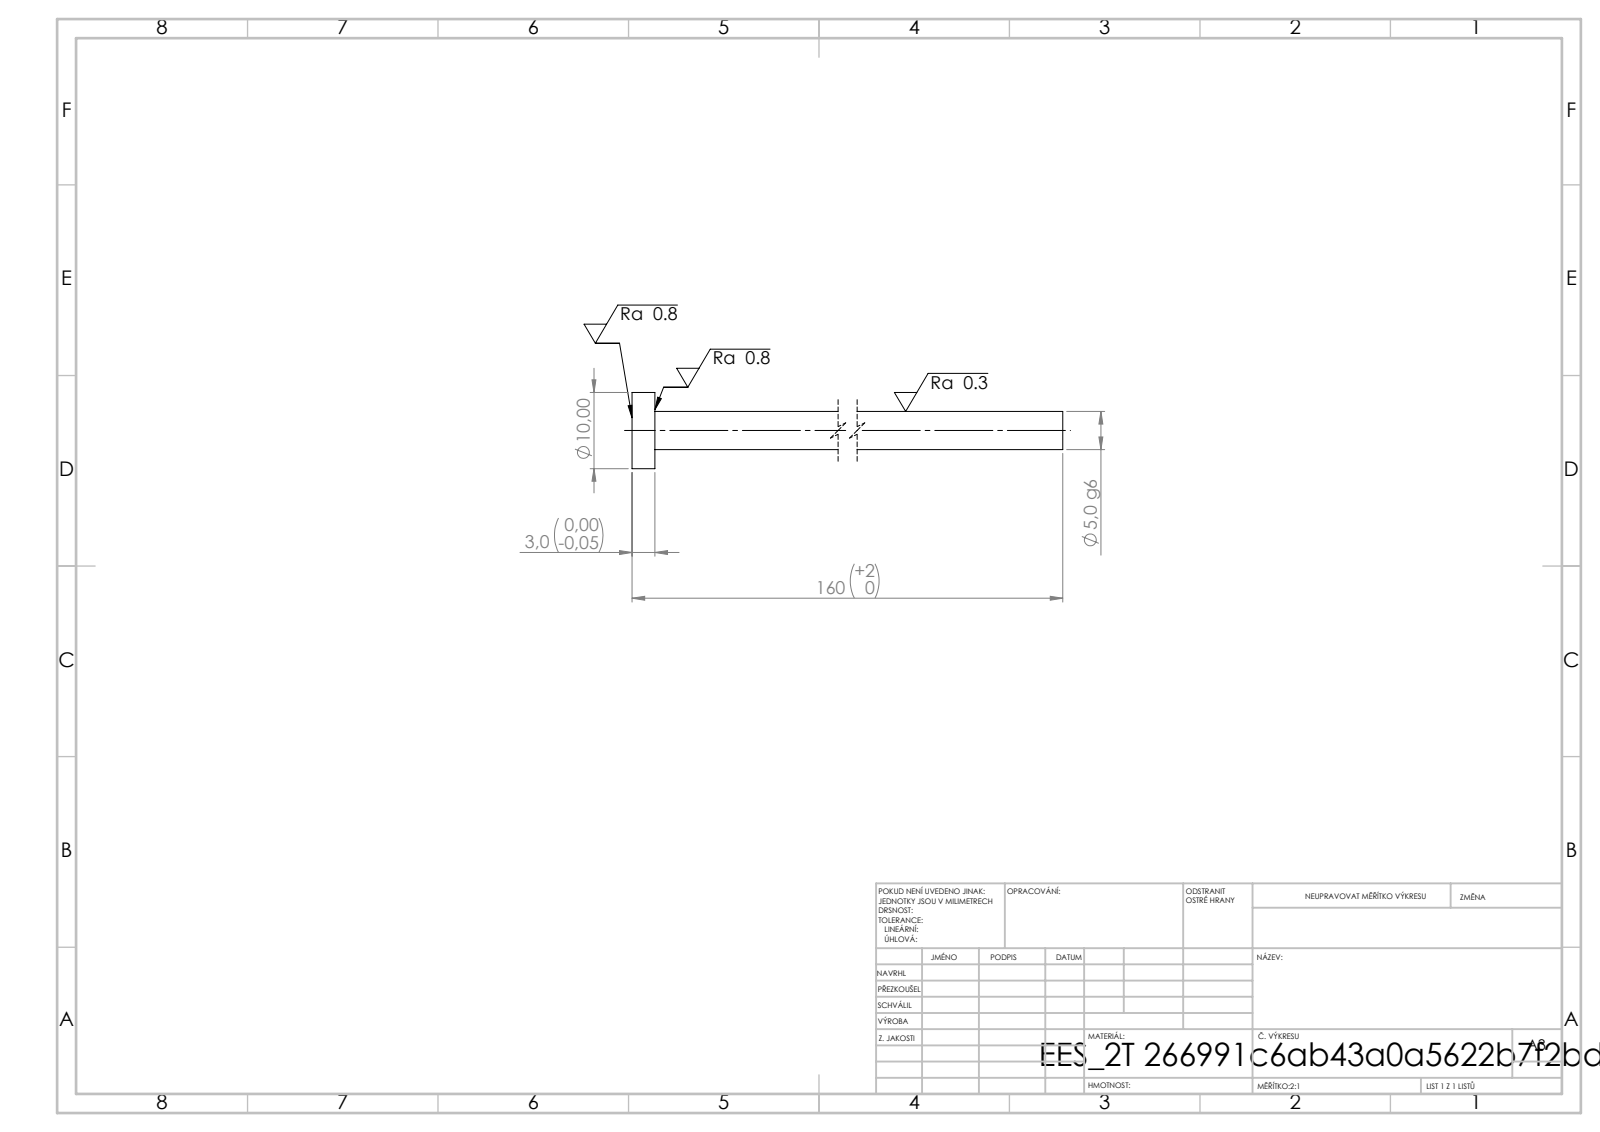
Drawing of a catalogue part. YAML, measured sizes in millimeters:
step_written_by: "SolidWorks 2019 (CONFIG_CONTROL_DESIGN)"
units: millimeters
bodies: {solids: 1, faces: 7, planar: 3, cylindrical: 4, other: 0}
overall_size: [160, 10, 10]
volume: 3318
surface_area: 2717
round_bosses_or_shafts:
  - {diameter: 10, count: 1}
  - {diameter: 5, count: 1}
face_to_face_distances: [3, 160, 157]
